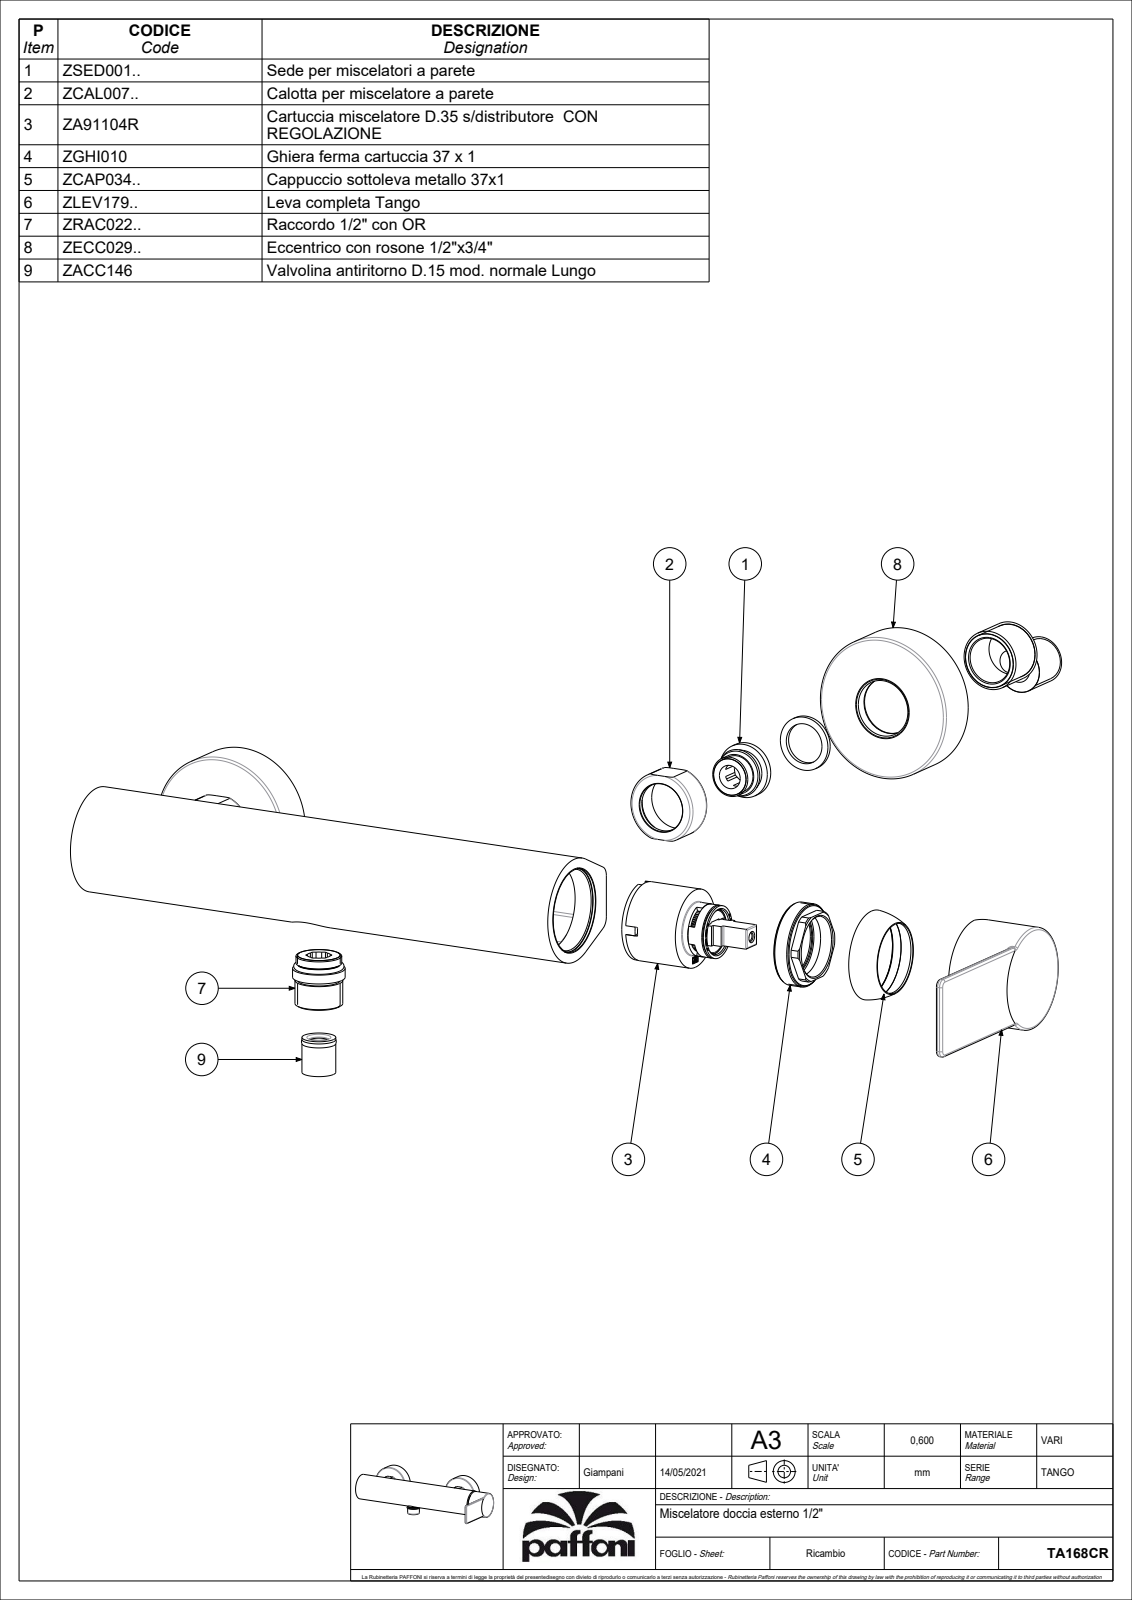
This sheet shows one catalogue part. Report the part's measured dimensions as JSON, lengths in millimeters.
{"part_name": "TA168CR", "step_written_by": "CREO PARAMETRIC BY PTC INC, 2020044 (CONFIG_CONTROL_DESIGN)", "units": "millimeters", "bodies": {"solids": 2, "faces": 471, "planar": 151, "cylindrical": 162, "other": 158}, "overall_size": [273.1, 143, 66.7], "volume_mm3": 347489, "surface_area_mm2": 128760, "round_holes": [[10.5, 2], [3, 1], [3.5, 1], [4.2, 1], [15.1, 1], [16, 1], [19, 1], [20, 1], [23.8, 1], [28.5, 1], [30, 1], [30.6, 1]], "round_bosses_or_shafts": [[63.5, 2], [17.7, 2], [45.5, 1], [23, 1], [20.9, 1], [7.6, 1], [5.5, 1]], "partial_cylinders_radius": [[1.5, 48], [1, 6], [0.5, 2], [1.3, 2], [3, 2], [5, 2], [15.6, 2], [18.5, 2]], "face_to_face_distances": [3.7, 20, 3.5, 49.2, 29.2, 35, 45.7, 25.7, 14.2, 15], "hole_center_spacings": [6, 75.1, 150, 225.1]}
